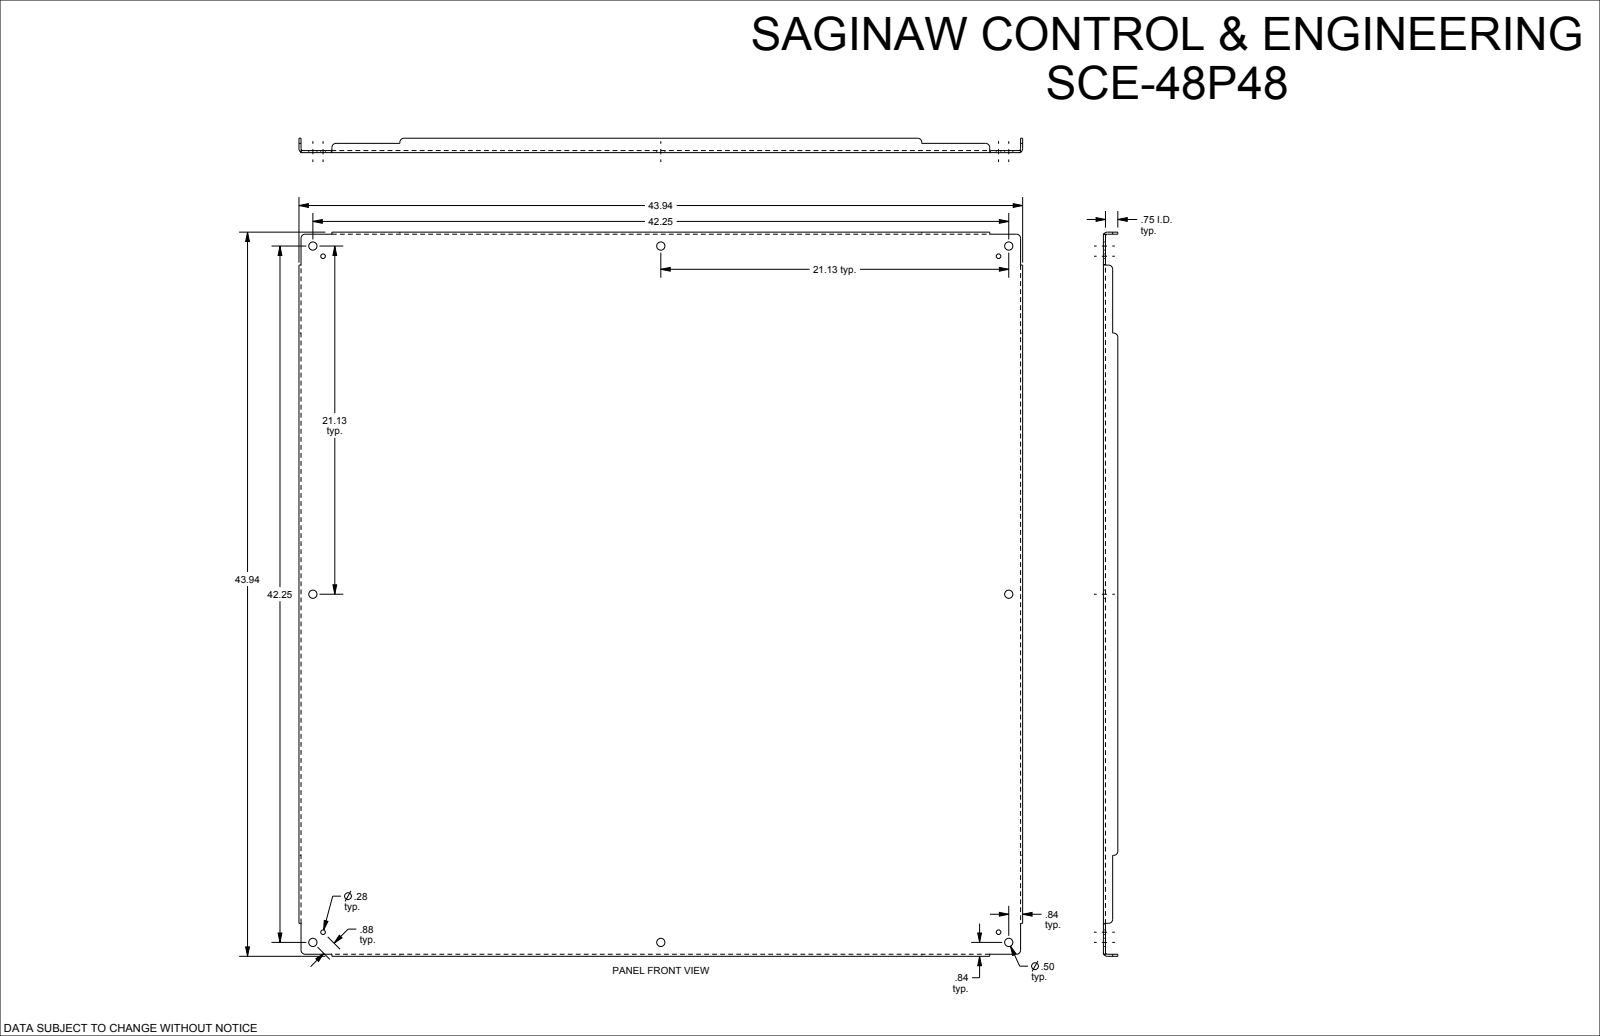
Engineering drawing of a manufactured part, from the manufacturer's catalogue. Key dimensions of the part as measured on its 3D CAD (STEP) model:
Part name (STEP PRODUCT): SCE-48P48
STEP written by: SolidWorks 2019 (CONFIG_CONTROL_DESIGN)
Units: inches
Bodies: 1 solid, 110 faces (46 planar, 40 cylindrical, 24 other)
Overall size (bounding box): 43.938 × 43.938 × 0.875
Volume: 253 in³ · Surface area: 4 072 in²
Round holes (diameter × count): ⌀0.5 ×8, ⌀0.281 ×4
Partial cylindrical surfaces — rounded edges, fillets, slot ends (radius × count): R0.25 ×12, R0.112 ×4, R0.237 ×4
Main face-to-face distances: 0.125, 0.125, 43.813, 43.687, 43.938, 0.75, 0.875, 0.312, 0.438, 0.563
Hole centre spacings: 20.516, 21.125, 41.636, 46.407, 47.237, 42.25, 0.875, 29.875
